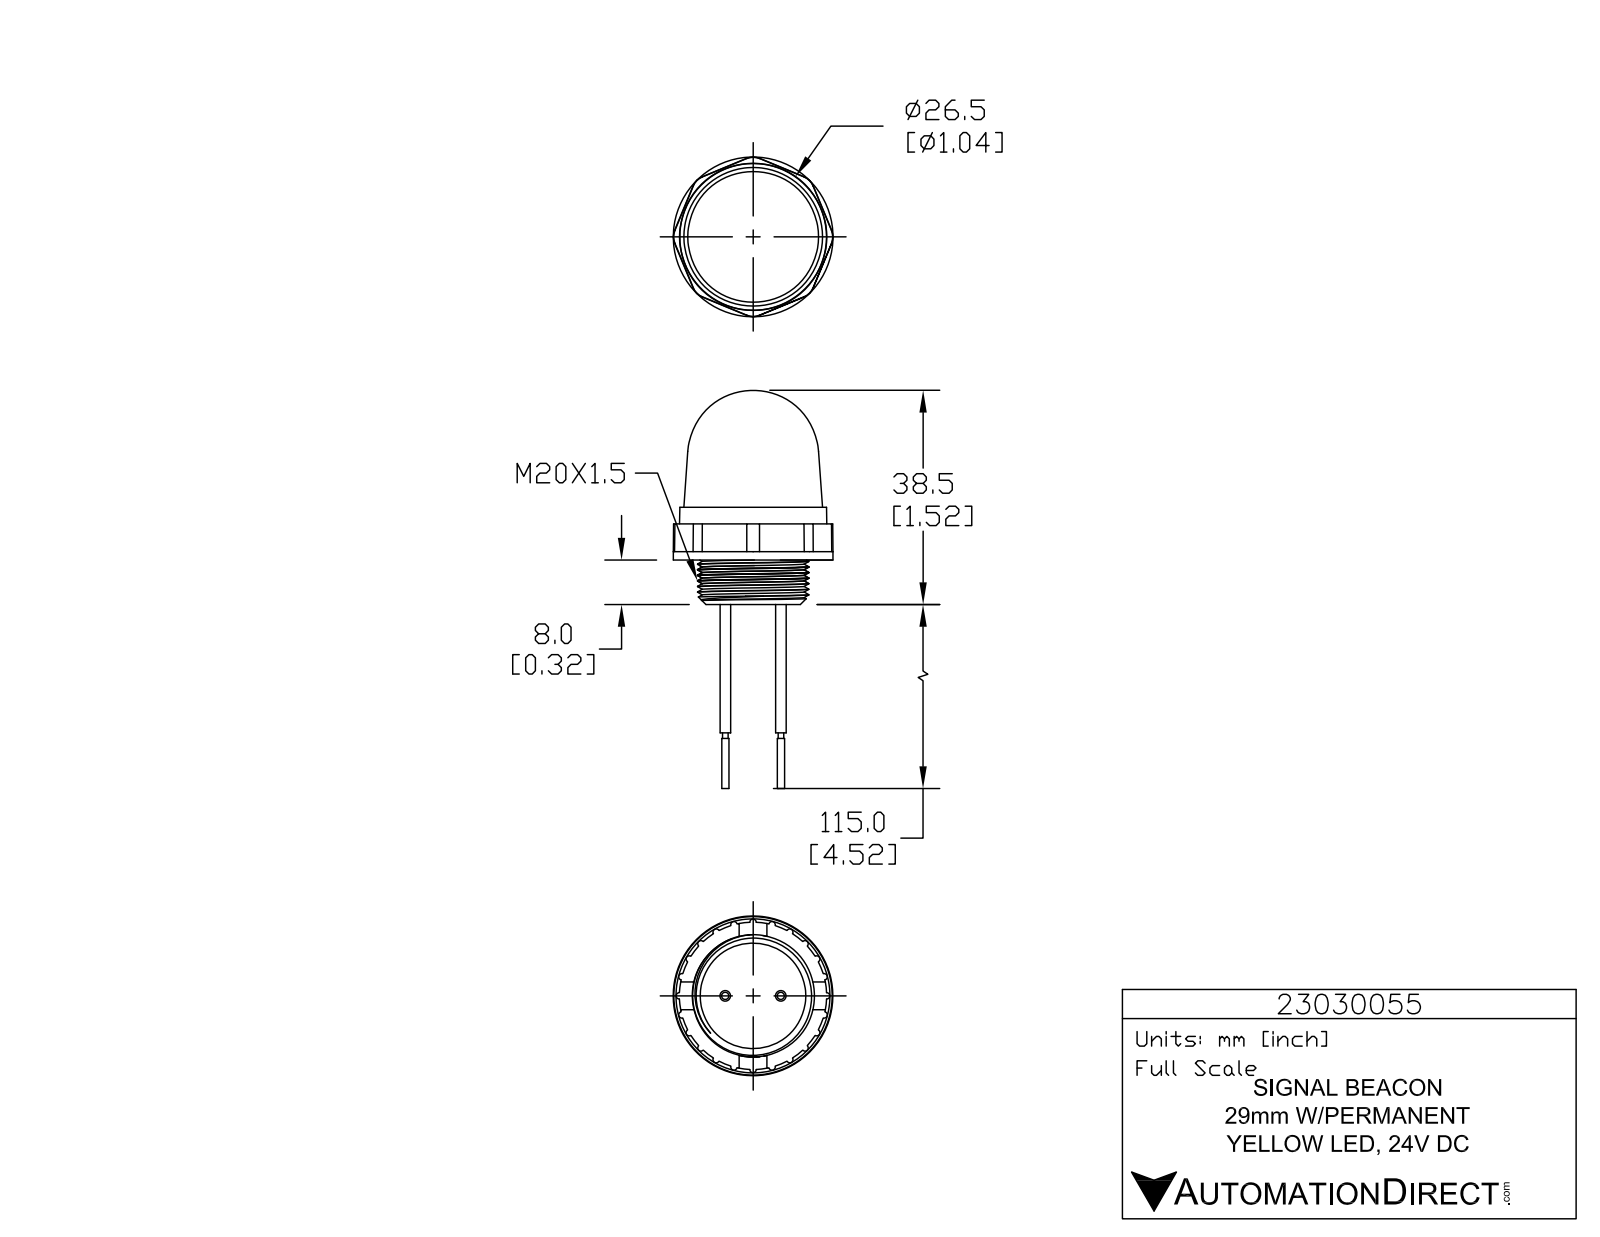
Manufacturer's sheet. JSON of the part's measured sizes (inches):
{"part_name": "23030055", "step_written_by": "SolidWorks 2017 (AUTOMOTIVE_DESIGN)", "units": "inches", "bodies": {"solids": 1, "faces": 844, "planar": 551, "cylindrical": 203, "other": 90}, "overall_size": [2.82, 1.131, 1.131], "volume_in3": 0.978, "surface_area_in2": 8.158, "round_holes": [[0.02, 3], [0.807, 1]], "round_bosses_or_shafts": [[0.113, 3], [0.028, 3], [0.075, 2], [0.051, 2], [0.039, 2], [1.131, 1], [1.122, 1], [0.894, 1]], "partial_cylinders_radius": [[0.118, 8], [0.004, 6], [0.004, 6], [0.004, 6], [0.065, 6], [0.005, 3], [0.007, 3], [0.008, 3]], "face_to_face_distances": [0.276, 0.374, 0.039, 0.315, 0.65, 0.638, 0.362, 0.689, 0.413, 0.051]}
